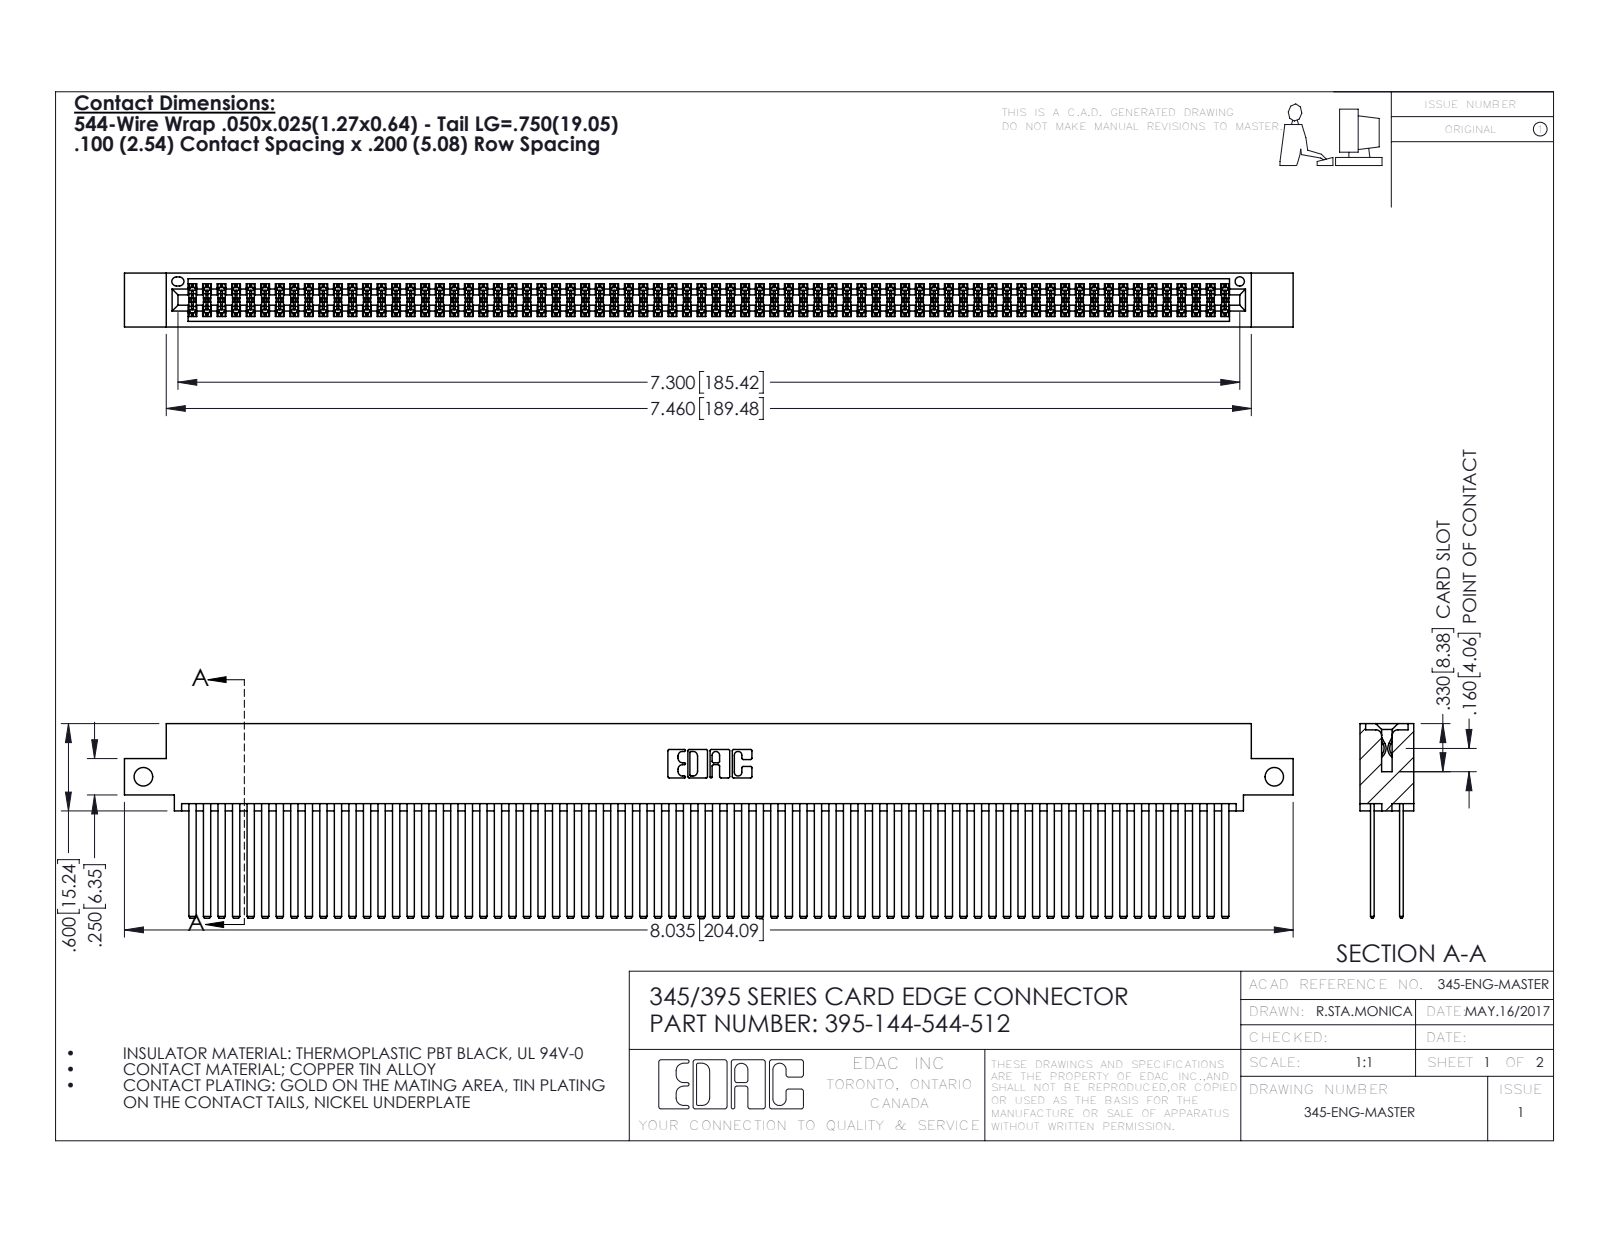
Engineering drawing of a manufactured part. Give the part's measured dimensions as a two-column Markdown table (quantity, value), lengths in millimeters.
| quantity | value |
| --- | --- |
| part name | 345 Part_0.110 Offset - Side Mount; 345-292-001_345-293-144; 395-144-544-512 |
| STEP written by | SolidWorks 2016 (CONFIG_CONTROL_DESIGN) |
| units | millimeters |
| bodies | 145 solids, 6466 faces (4260 planar, 2206 cylindrical, 0 other) |
| overall size | 204.1 × 34 × 9.4 |
| volume | 21 960 mm³ |
| surface area | 38 920 mm² |
| round holes (diameter × count) | 3.3 × 2, 1.6 × 1 |
| partial cylindrical surfaces (radius × count) | 0.2 × 216, 0.3 × 22, 0.2 × 6, 0.8 × 6, 0.7 × 3, 0.4 × 2, 0.5 × 2, 0.6 × 2 |
| main face-to-face distances | 5.1, 0.6, 7.6, 1.8, 2.5, 6.9, 5.7, 4.4, 9.4, 3.8 |
| hole center spacings | 197.5 |
